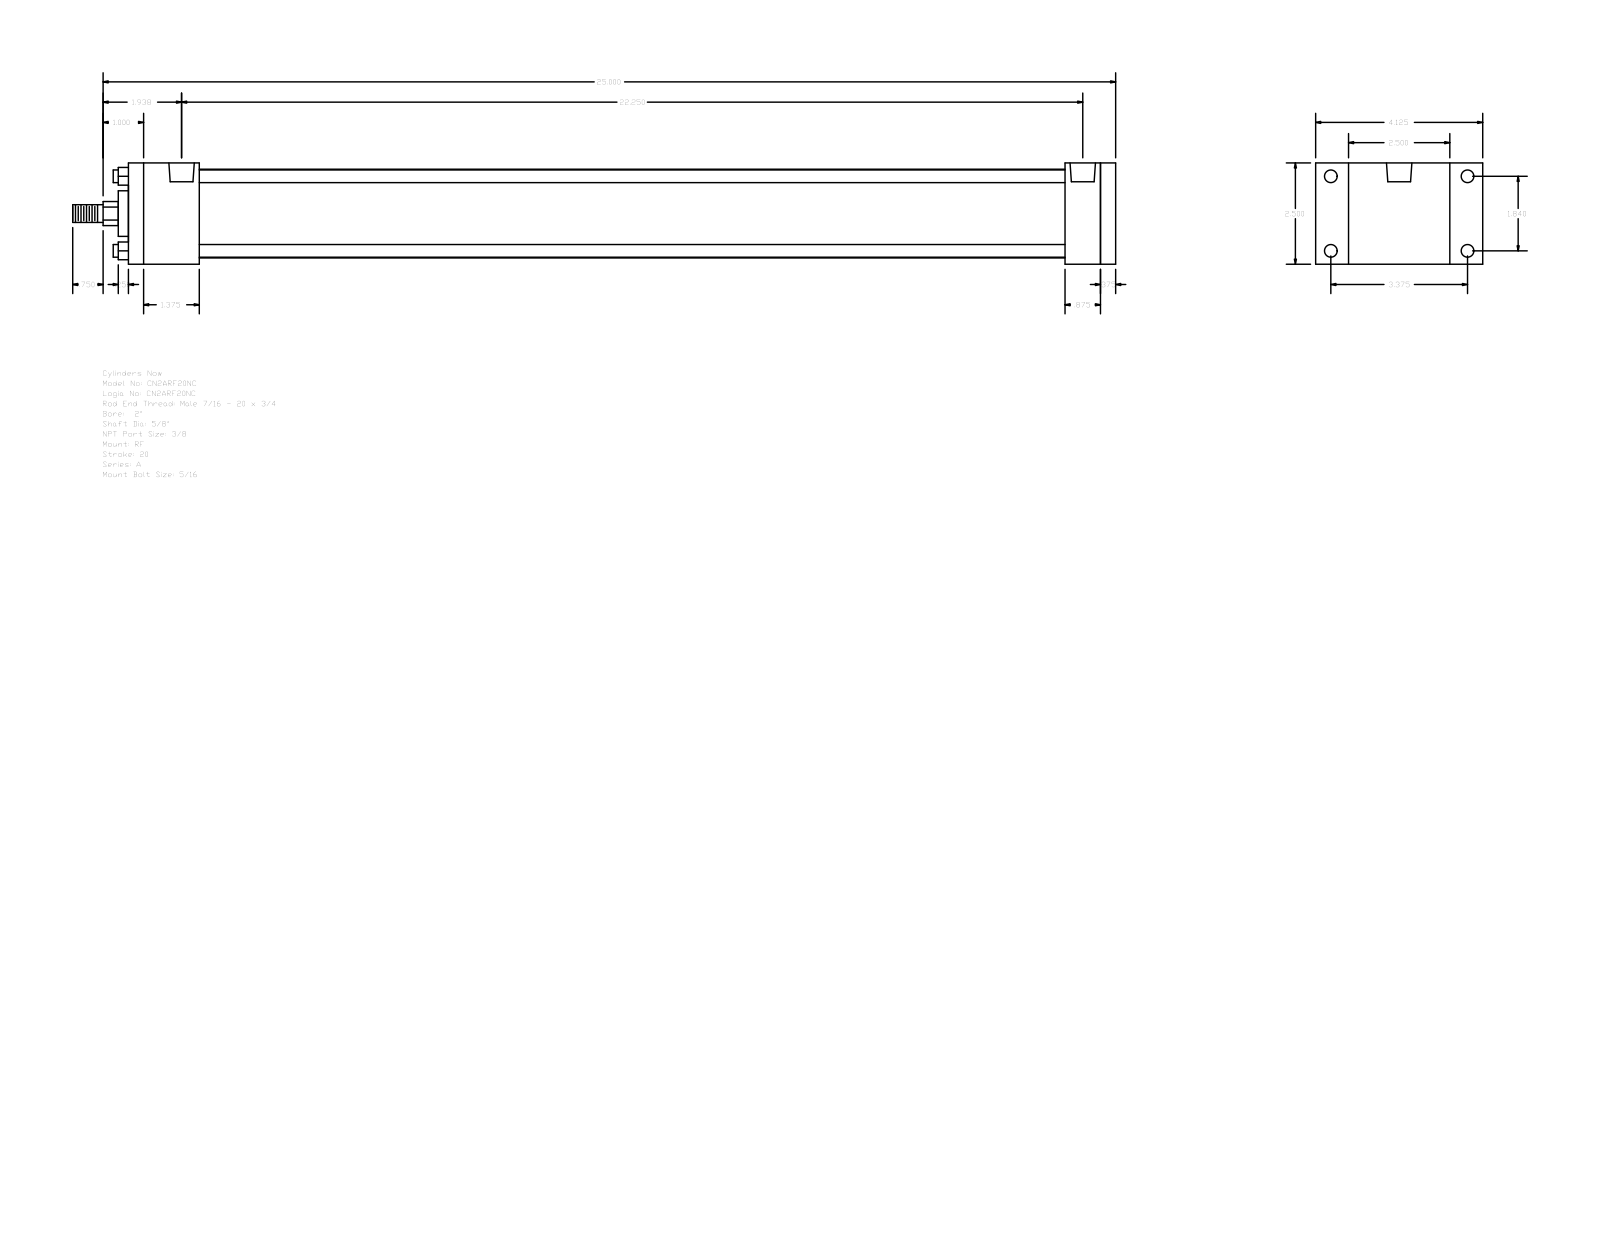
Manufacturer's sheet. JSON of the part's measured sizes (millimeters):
{"part_name": "A_RF__0200_0.625", "step_written_by": "GSSL Pune (CONFIG_CONTROL_DESIGN)", "units": "millimeters", "bodies": {"solids": 0, "faces": 92, "planar": 64, "cylindrical": 28, "other": 0}, "overall_size": [654.05, 104.78, 63.5], "round_holes": [[5.56, 4], [7.94, 4], [15.93, 2]], "round_bosses_or_shafts": [[7.94, 4], [55.63, 1], [28.57, 1], [15.88, 1], [11.11, 1]], "partial_cylinders_radius": [[7.54, 1]], "face_to_face_distances": [63.5, 619.12, 609.6, 9.52, 44.45, 565.15, 574.67, 587.37, 542.92, 22.23], "hole_center_spacings": [46.74, 85.72, 97.63, 557.2, 3.97, 3.98, 561.17, 561.18]}
